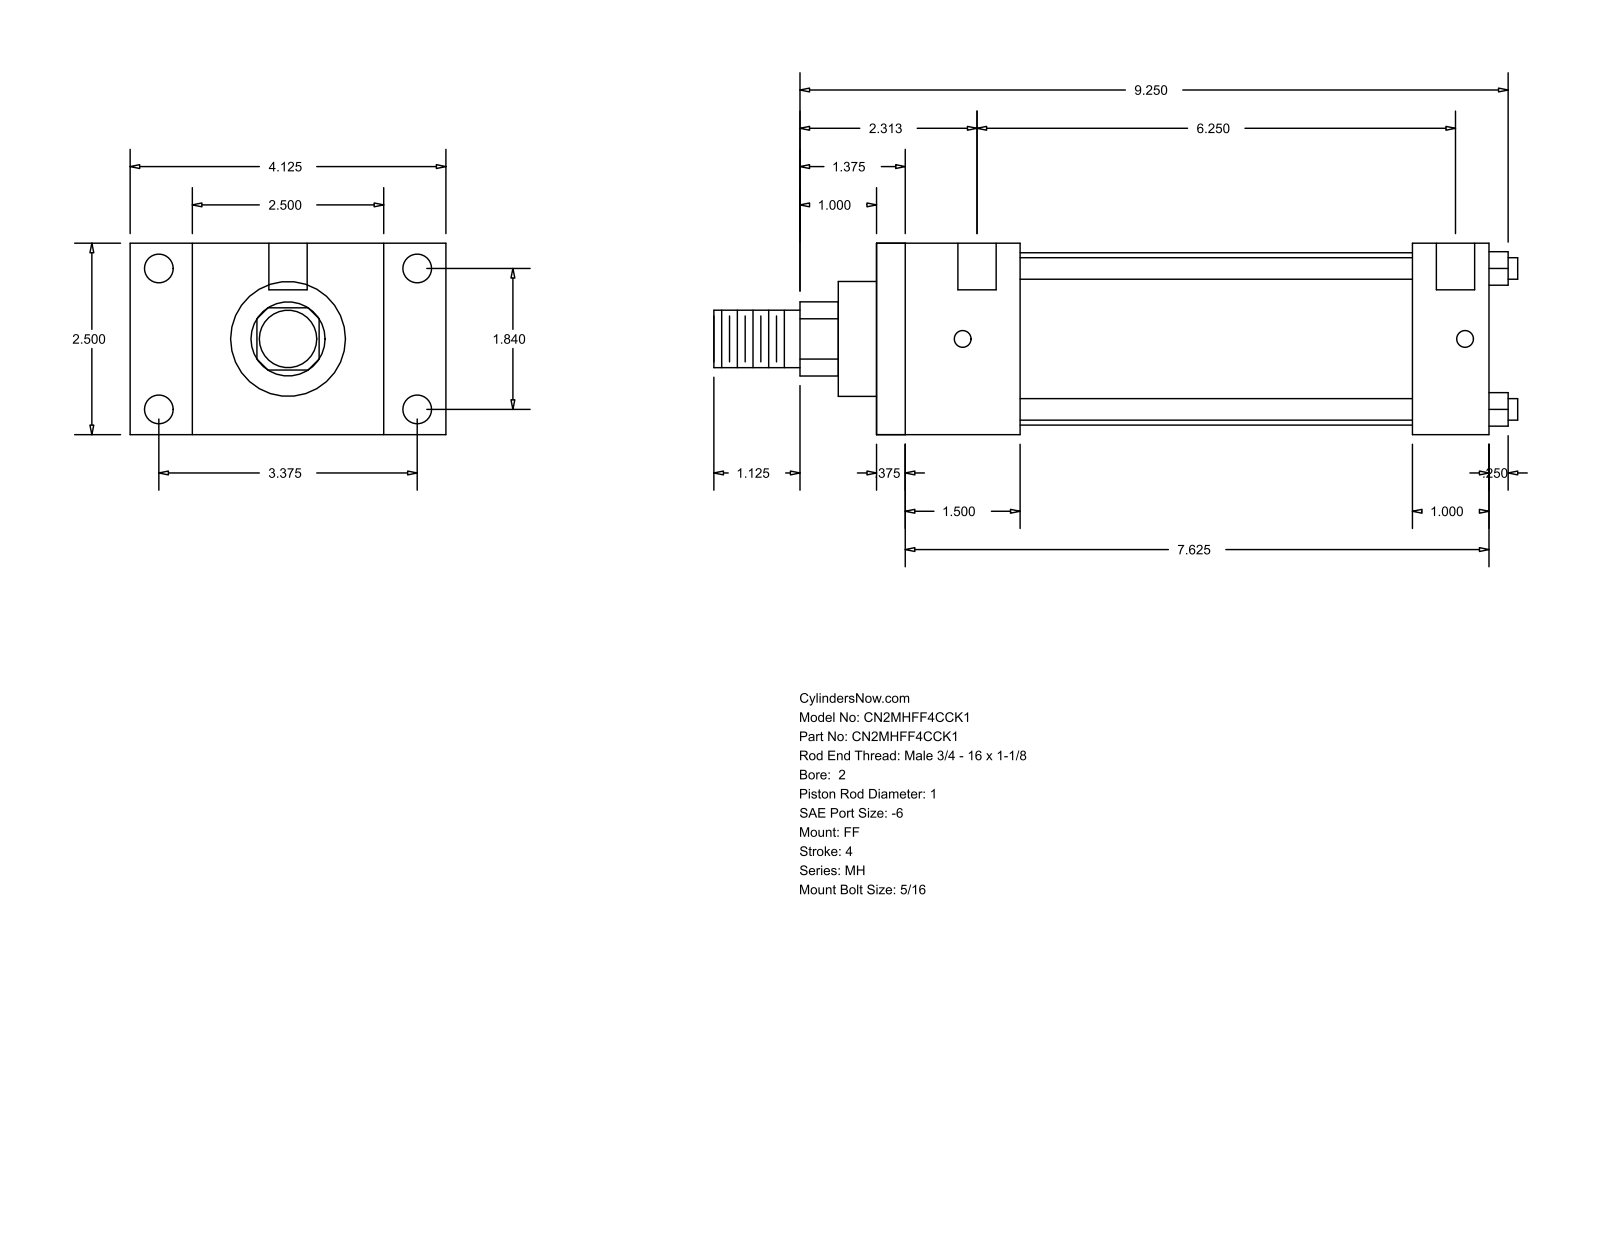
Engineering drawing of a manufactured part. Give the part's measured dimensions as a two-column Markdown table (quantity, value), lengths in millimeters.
| quantity | value |
| --- | --- |
| part name | MH_FF__0200_1 |
| STEP written by | GSSL Pune (CONFIG_CONTROL_DESIGN) |
| units | millimeters |
| bodies | 0 solids, 92 faces (64 planar, 28 cylindrical, 0 other) |
| overall size | 266.7 × 104.78 × 63.5 |
| round holes (diameter × count) | 5.56 × 4, 9.53 × 4, 12.7 × 2 |
| round bosses / shafts (diameter × count) | 7.14 × 4, 57.15 × 1, 38.1 × 1, 25.4 × 1, 19.05 × 1 |
| partial cylindrical surfaces (radius × count) | 12.29 × 1 |
| main face-to-face distances | 63.5, 203.2, 9.52, 193.68, 20.64, 25.4, 47.63, 177.8, 38.11, 168.28 |
| hole center spacings | 46.74, 85.72, 97.63, 166.68, 3.17, 4.76, 158.75, 161.92 |
